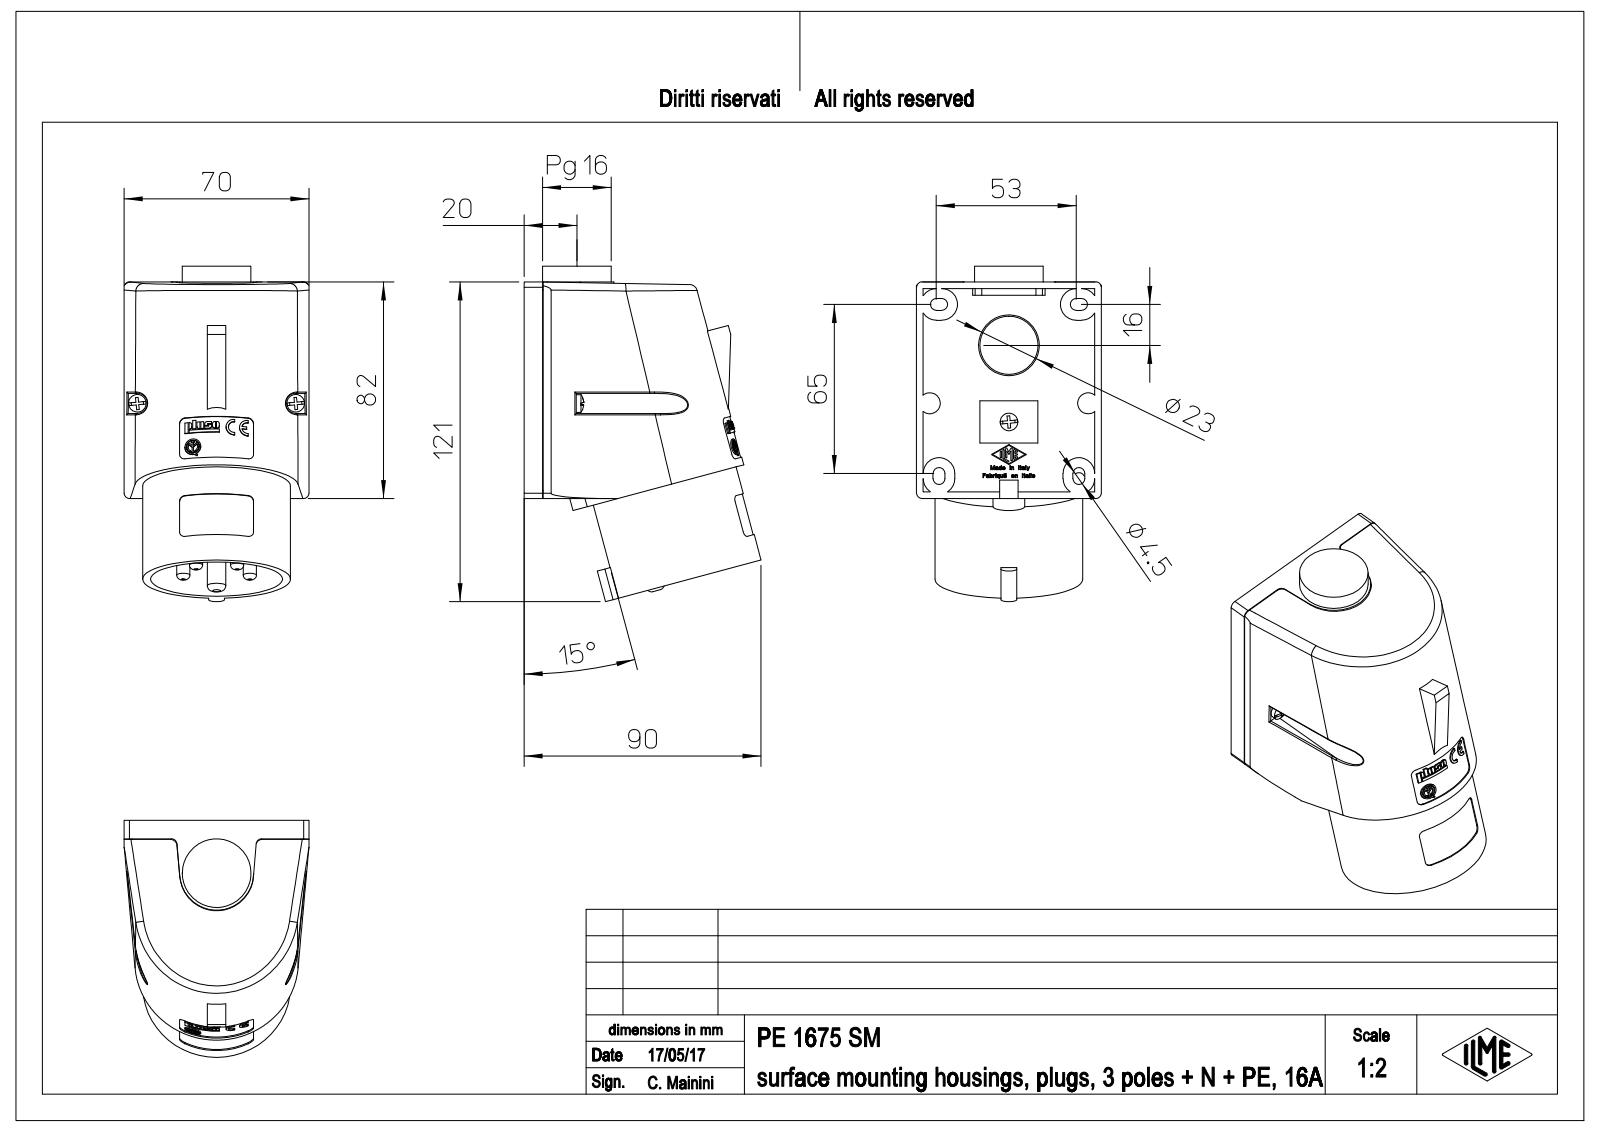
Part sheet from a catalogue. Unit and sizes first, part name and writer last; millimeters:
Units: millimetres
Overall size (bounding box): 127.04 × 89.75 × 70
Round holes (diameter × count): ⌀3.2 ×2, ⌀4.3 ×2, ⌀4.5 ×2, ⌀3 ×1, ⌀5.04 ×1, ⌀21.3 ×1, ⌀23 ×1, ⌀24 ×1, ⌀50 ×1
Round bosses / shafts (diameter × count): ⌀5 ×6, ⌀6.7 ×5, ⌀26 ×2, ⌀56 ×1, ⌀49 ×1, ⌀7 ×1, ⌀6 ×1
Partial cylindrical surfaces — rounded edges, fillets, slot ends (radius × count): R0.25 ×15, R2 ×14, R6 ×13, R0.5 ×9, R0.86 ×9, R2.25 ×8, R4 ×8, R1 ×6
Main face-to-face distances: 2.5, 6.2, 3.7, 3.5, 6, 1, 7.2, 7, 82, 3
Hole centre spacings: 37.2, 60
Volume: 341 934 mm³ · Surface area: 67 379 mm²
Bodies: 1 solid, 1845 faces (1561 planar, 188 cylindrical, 96 other)
Part name (STEP PRODUCT): PE_1675_SM
STEP written by: PTC Creo Elements/Direct Modeling 19.0E 27-Jun-2016 (C) Parametric Technology GmbH (AUTOMOTIVE_DESIGN)
